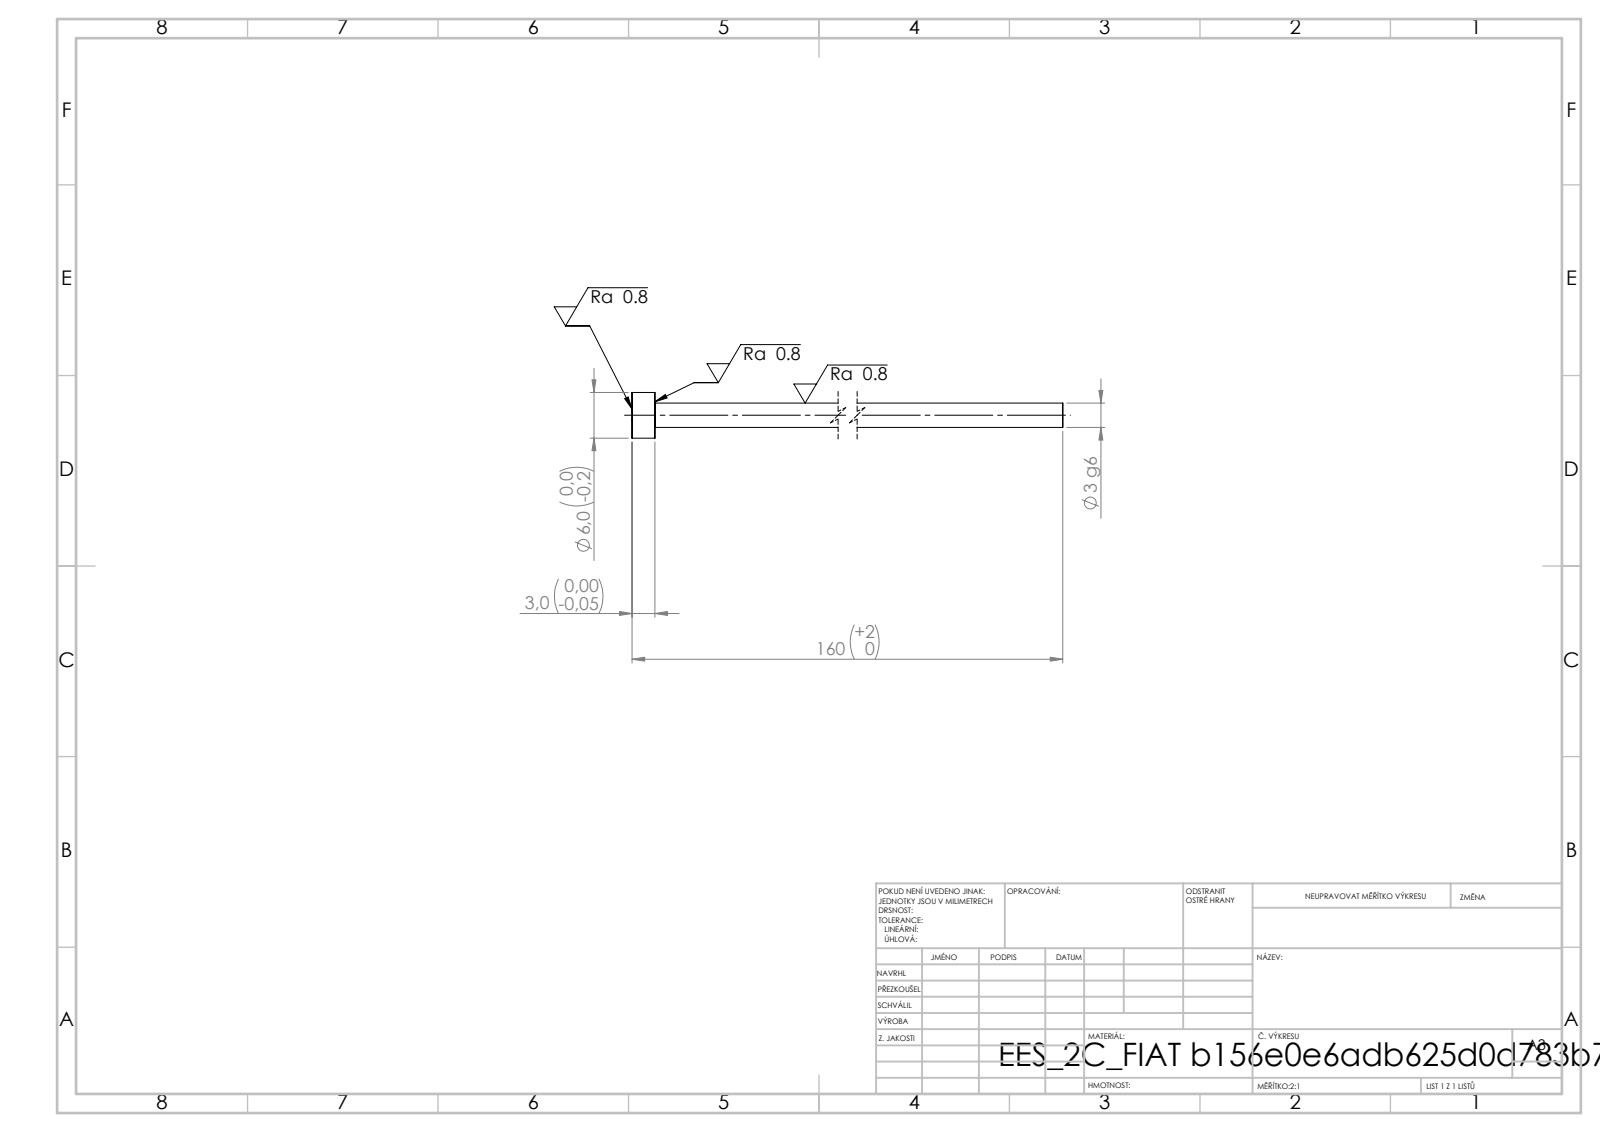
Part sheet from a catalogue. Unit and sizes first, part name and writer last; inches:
Units: inches
Overall size (bounding box): 6.299 × 0.236 × 0.236
Round bosses / shafts (diameter × count): ⌀0.236 ×1, ⌀0.126 ×1
Main face-to-face distances: 0.118, 6.299, 6.181
Volume: 0.082 in³ · Surface area: 2.621 in²
Bodies: 1 solid, 7 faces (3 planar, 4 cylindrical, 0 other)
STEP written by: SolidWorks 2019 (CONFIG_CONTROL_DESIGN)
